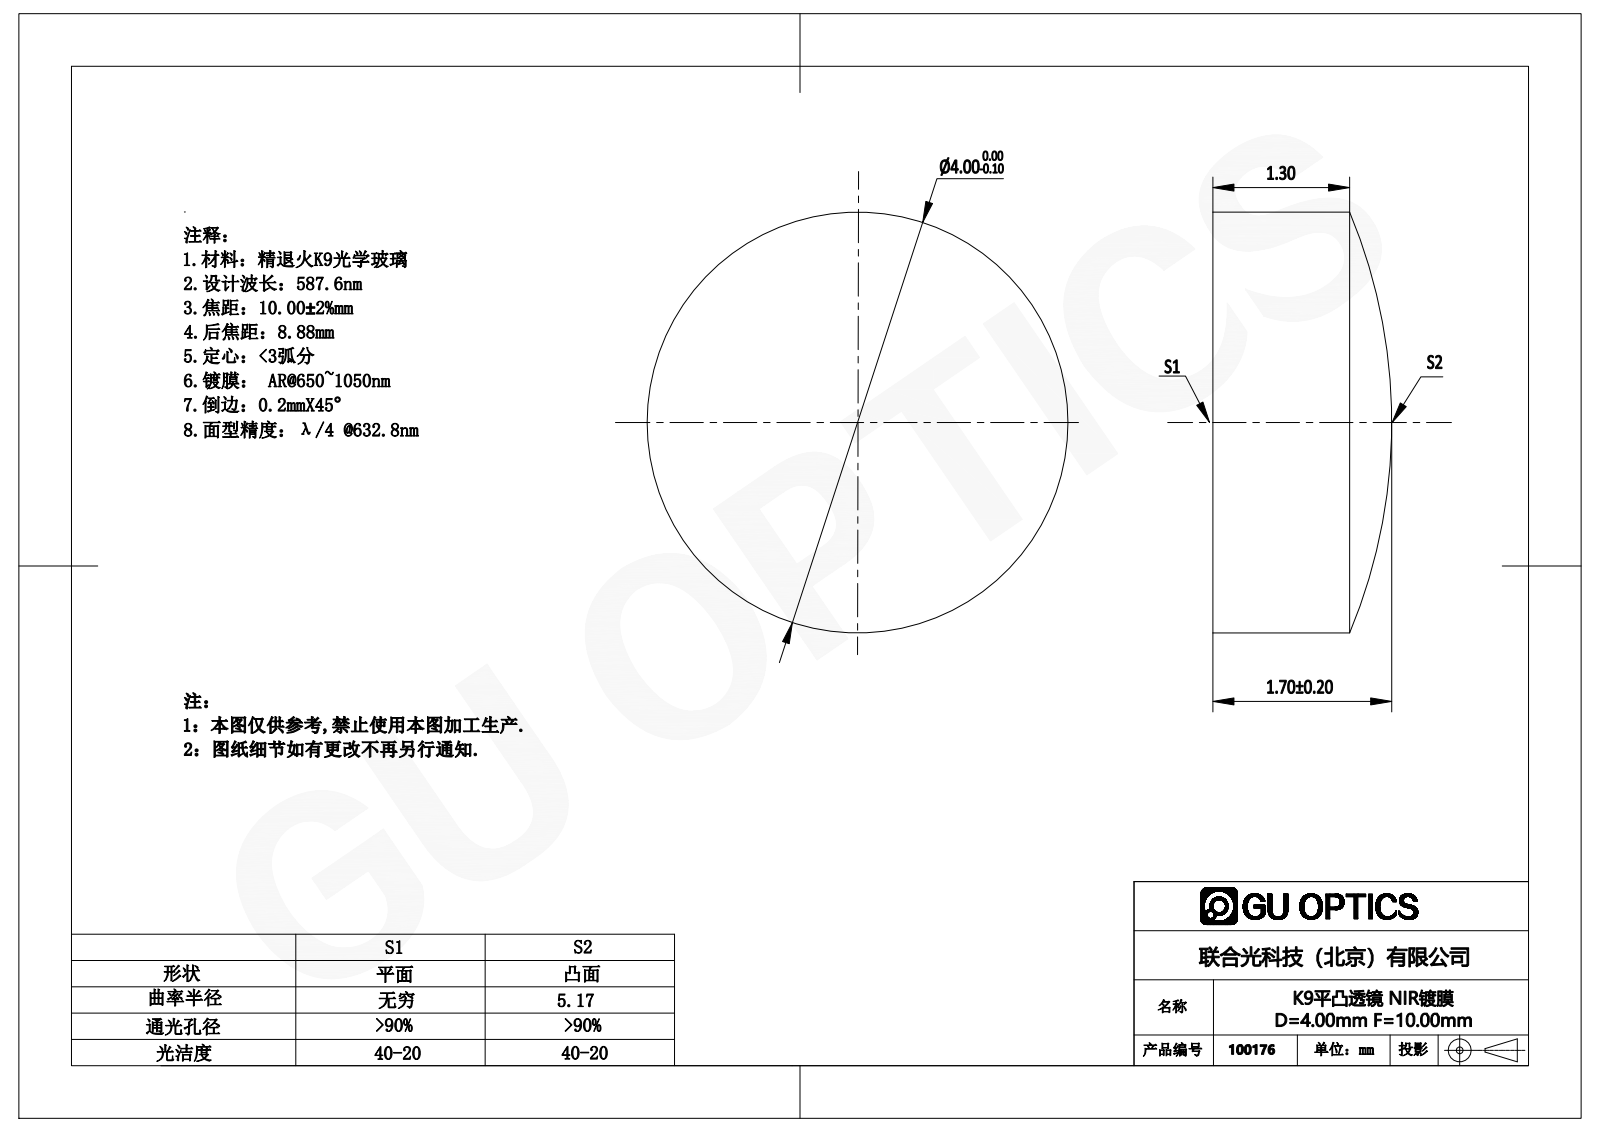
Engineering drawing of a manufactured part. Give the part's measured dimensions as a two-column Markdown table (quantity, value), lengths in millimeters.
| quantity | value |
| --- | --- |
| part name | 100176 |
| STEP written by | SolidWorks 2016 (AUTOMOTIVE_DESIGN) |
| units | millimeters |
| bodies | 1 solid, 5 faces (1 planar, 2 cylindrical, 2 other) |
| overall size | 4 × 4 × 1.7 |
| volume | 19 mm³ |
| surface area | 42 mm² |
| round bosses / shafts (diameter × count) | 4 × 1 |
